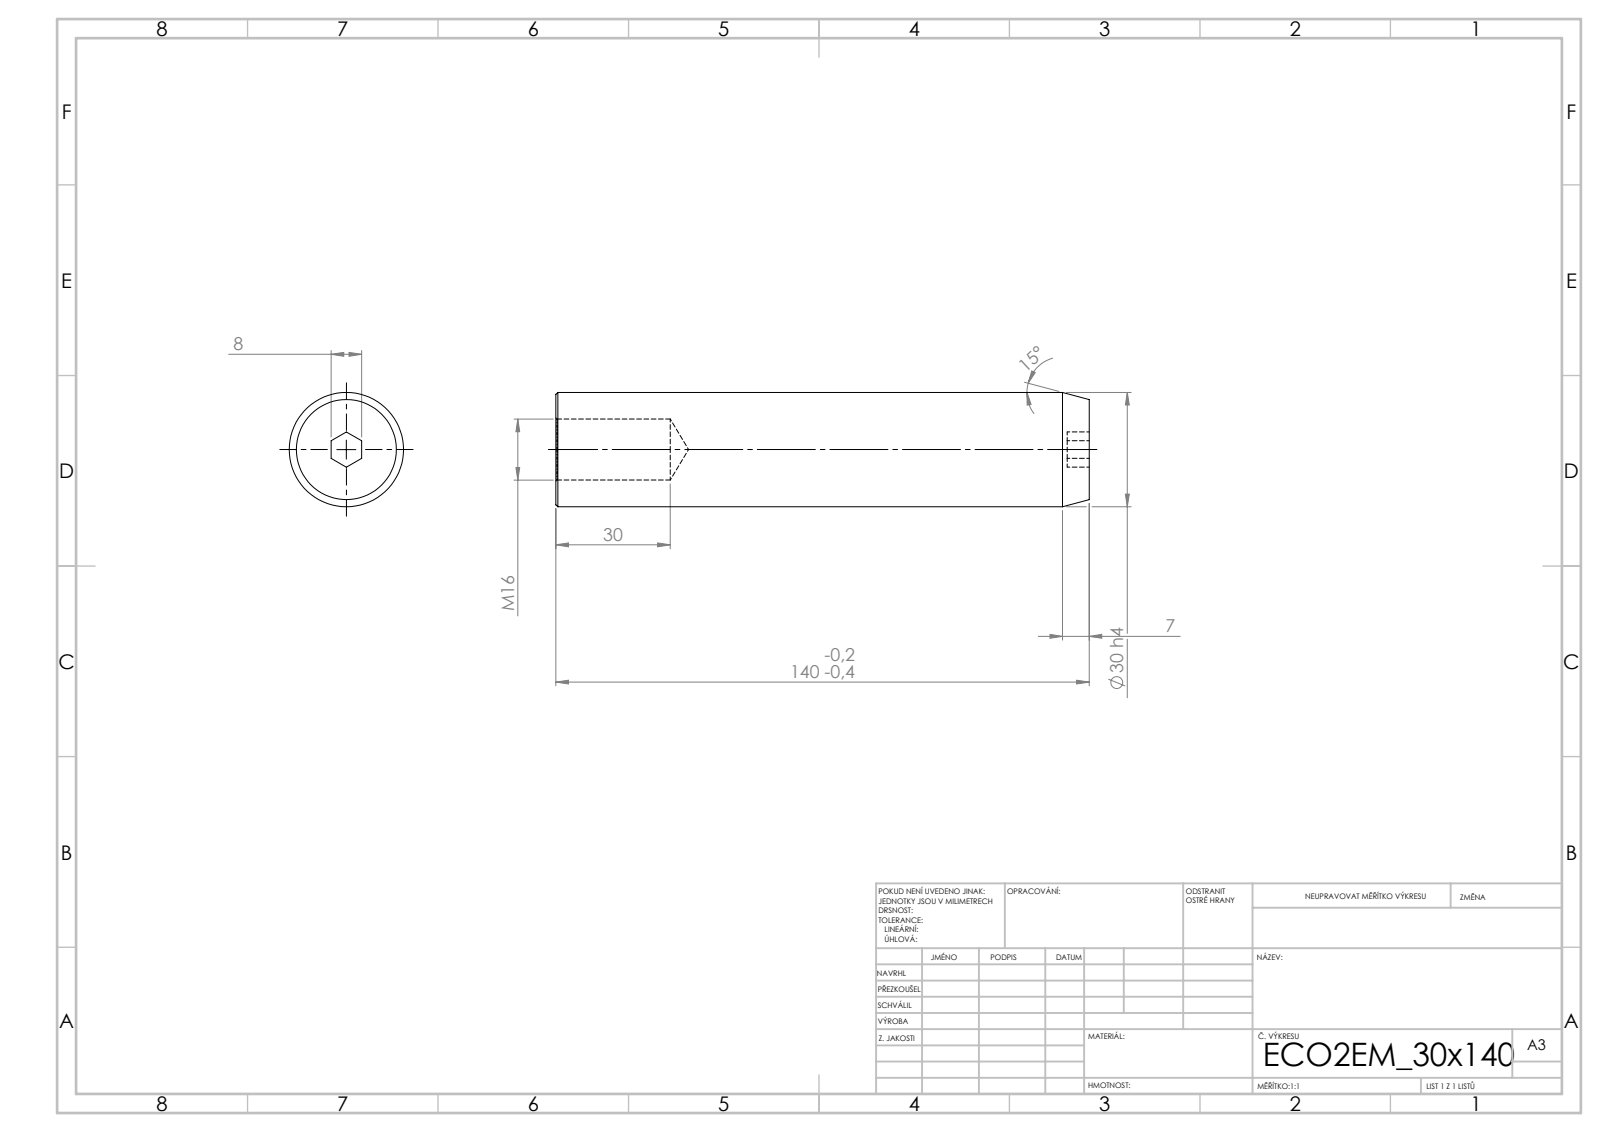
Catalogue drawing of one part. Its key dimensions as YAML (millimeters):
step_written_by: "SolidWorks 2019 (CONFIG_CONTROL_DESIGN)"
units: millimeters
bodies: {solids: 1, faces: 21, planar: 9, cylindrical: 4, other: 8}
overall_size: [140, 30, 30]
volume: 91679
surface_area: 16091
round_holes:
  - {diameter: 16, count: 1}
round_bosses_or_shafts:
  - {diameter: 30, count: 1}
face_to_face_distances: [140, 8, 5.8, 134.2]
